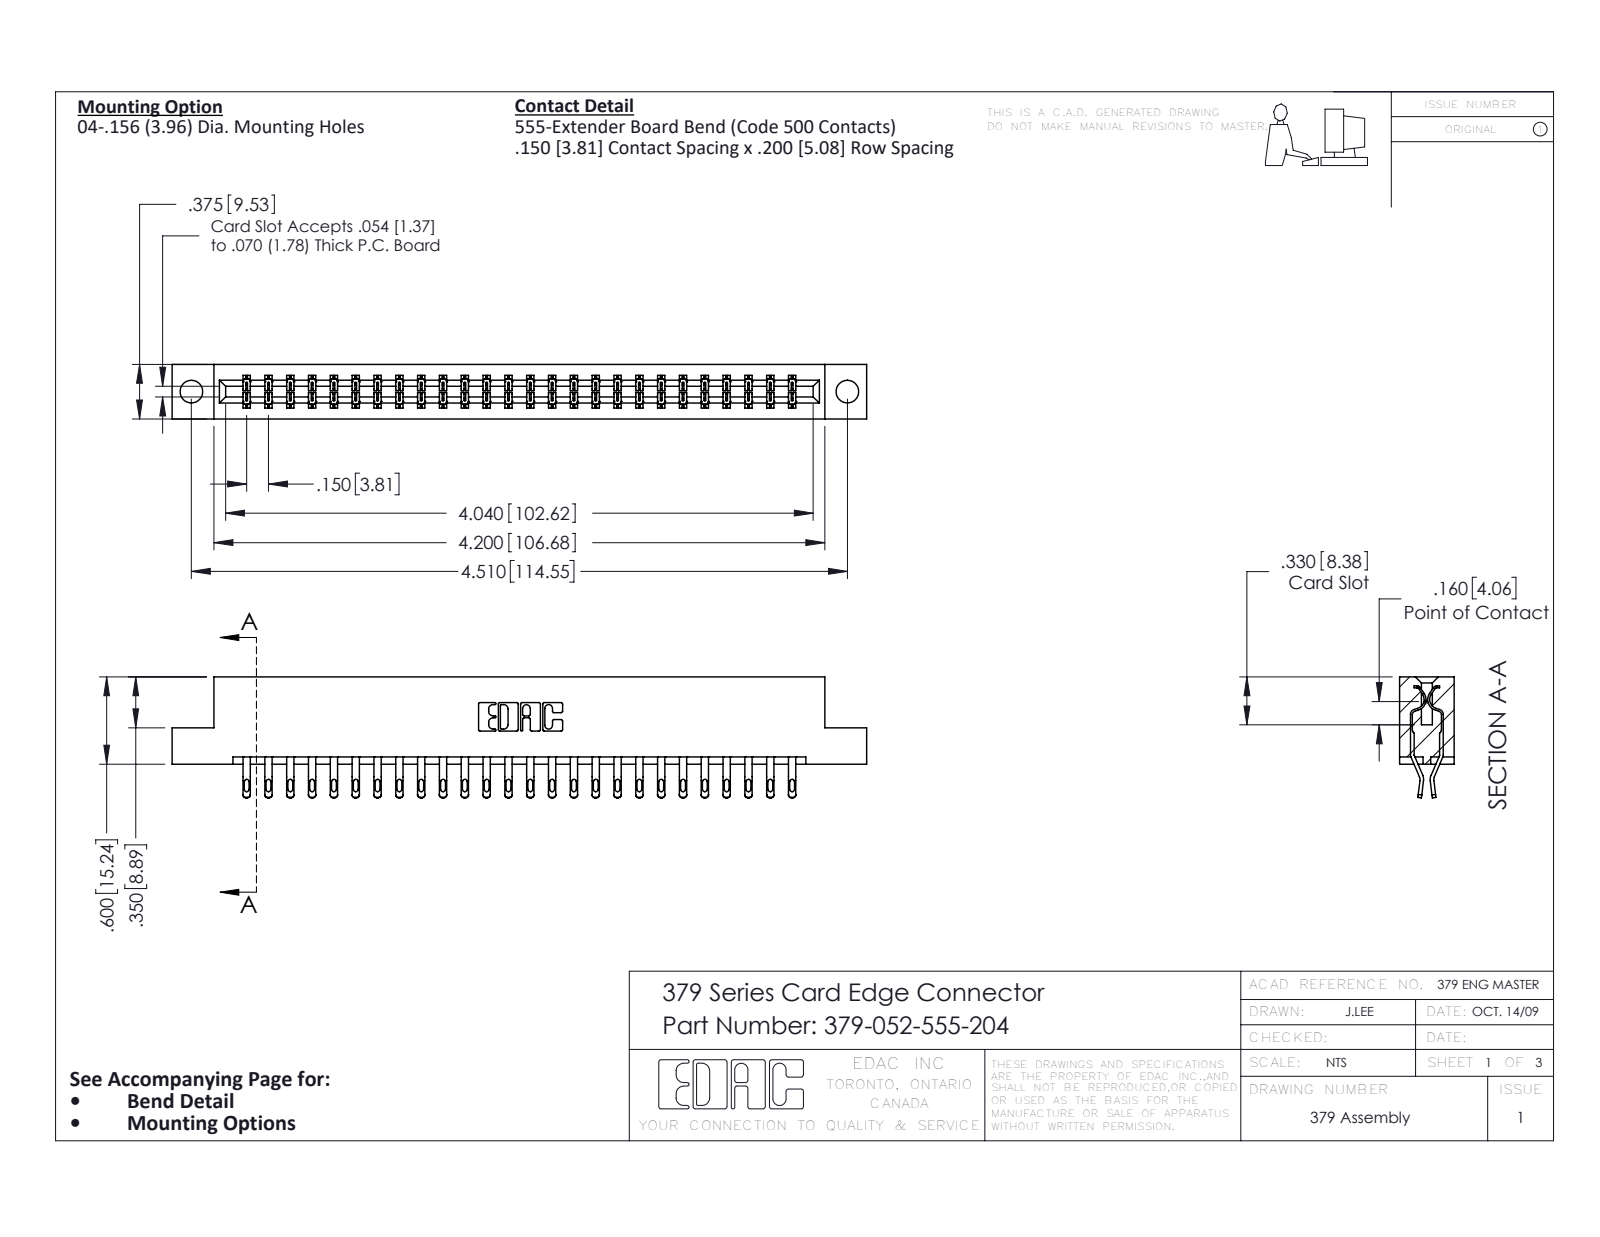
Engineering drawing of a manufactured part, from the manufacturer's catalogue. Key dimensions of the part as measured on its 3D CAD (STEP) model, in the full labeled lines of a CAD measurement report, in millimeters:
Part name (STEP PRODUCT): 379-052-555-204; 379 Part_Flush - .156 Dia - TH; 345-292-001_555 Tail
STEP written by: SolidWorks 2016 (CONFIG_CONTROL_DESIGN)
Units: millimetres
Bodies: 53 solids, 3130 faces (1838 planar, 1292 cylindrical, 0 other)
Overall size (bounding box): 121.3 × 21.1 × 9.5
Volume: 12 800 mm³ · Surface area: 14 580 mm²
Round holes (diameter × count): ⌀4 ×2
Partial cylindrical surfaces — rounded edges, fillets, slot ends (radius × count): R0.4 ×104, R0.5 ×104, R0.2 ×78, R0.3 ×22, R0.2 ×6, R0.8 ×6, R0.7 ×3, R0.3 ×2
Main face-to-face distances: 7.6, 1.9, 9.5, 5.1, 2.5, 5.7, 14, 3.8, 1.3, 15.2
Hole centre spacings: 114.6
